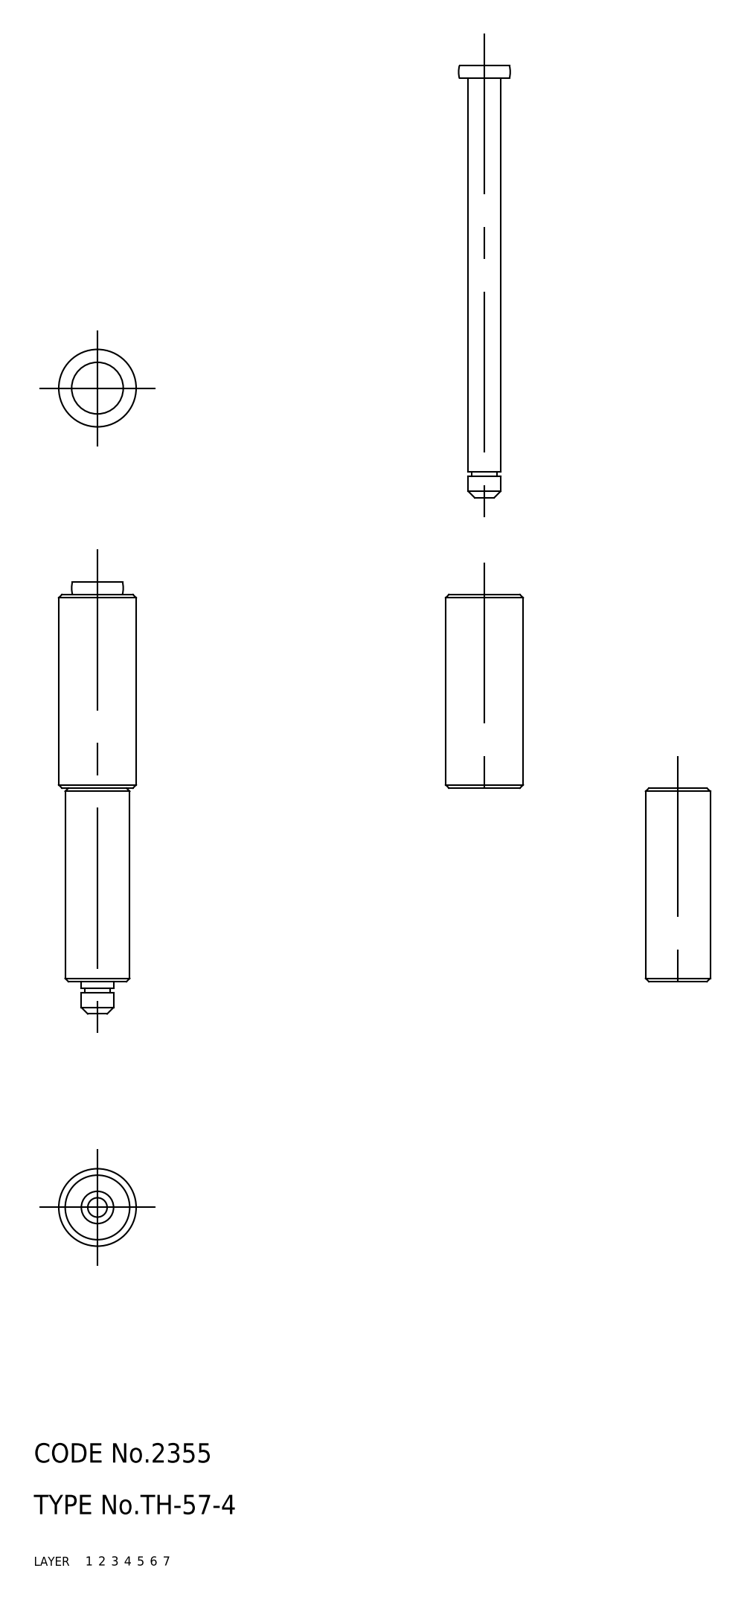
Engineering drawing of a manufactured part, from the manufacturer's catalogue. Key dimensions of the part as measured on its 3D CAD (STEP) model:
Part name (STEP PRODUCT): shaft; collar_B; collar_A; TH_57_4_11733_36
STEP written by: CADfix (AUTOMOTIVE_DESIGN)
Units: millimetres
Bodies: 3 solids, 34 faces (0 planar, 0 cylindrical, 34 other)
Overall size (bounding box): 67 × 12 × 12
Volume: 5 928 mm³ · Surface area: 4 448 mm²
